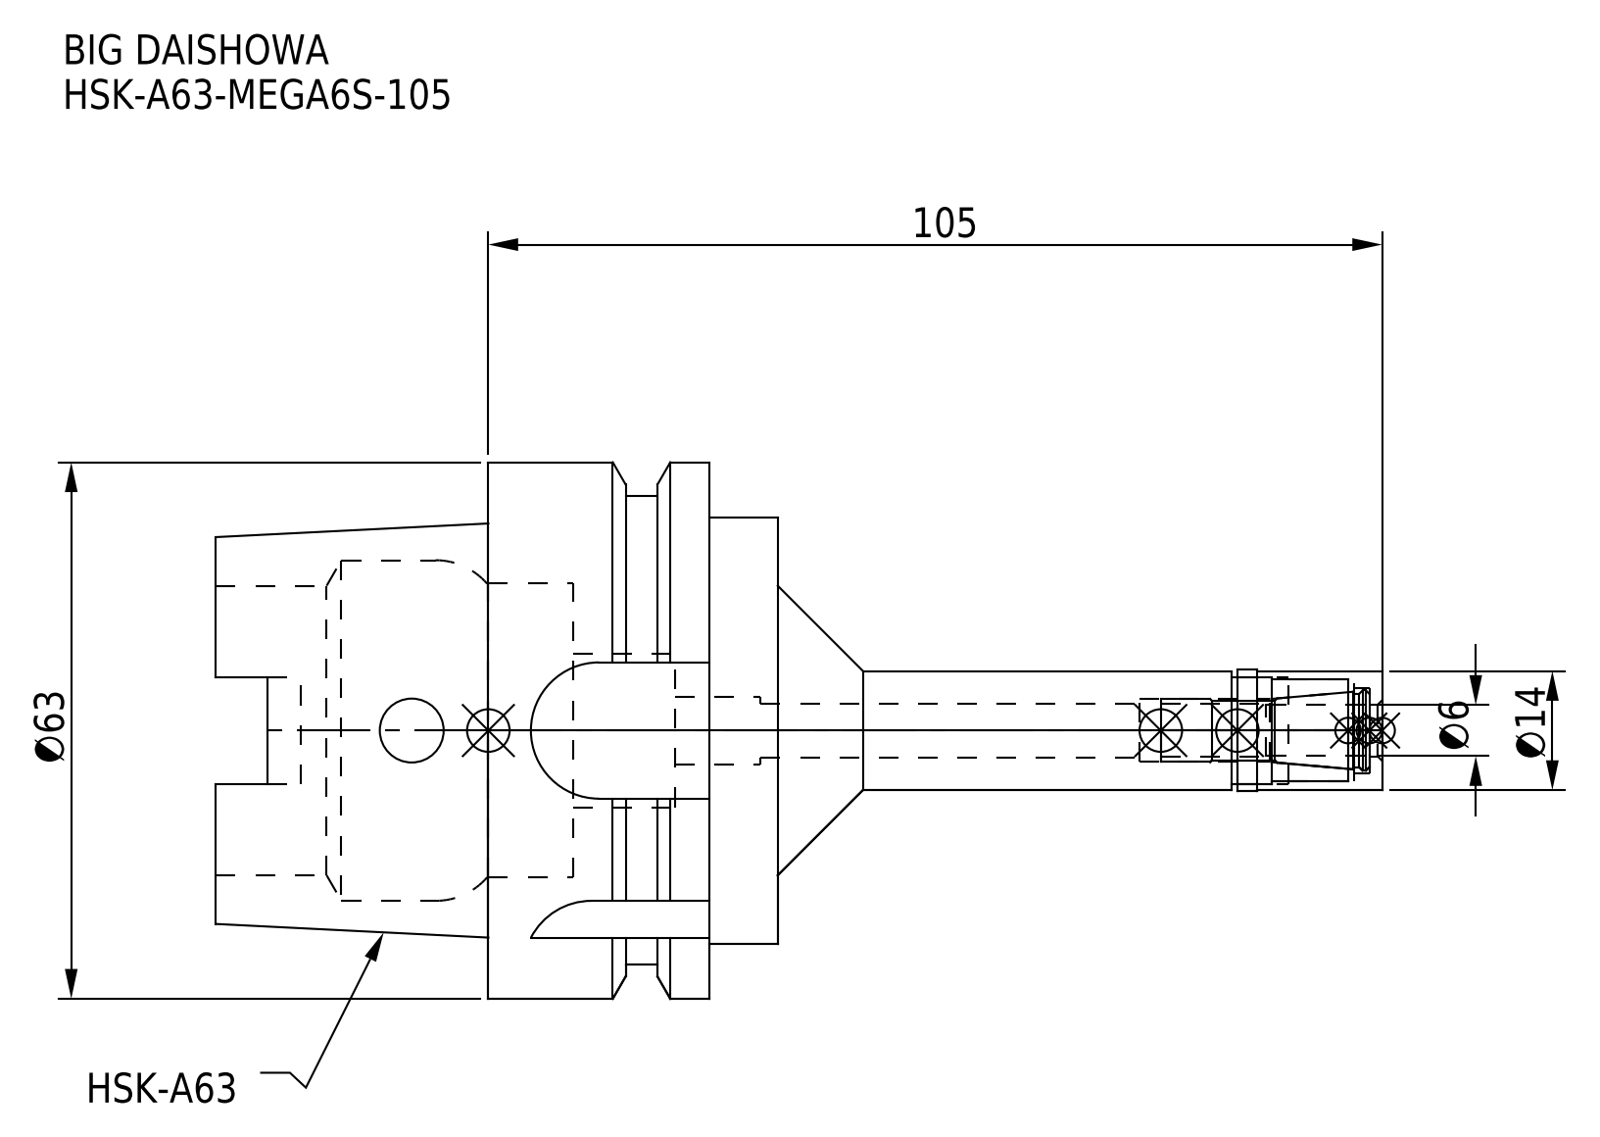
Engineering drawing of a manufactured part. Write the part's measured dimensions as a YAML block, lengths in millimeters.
part_name: "DXF_TEMP_ASSY_ASM_4_ASM.stp; HSK-A63-MEGA6S-105-060-FreeParts; HSK-A63-MEGA6S-105_1.stp; HSK-A63-MEGA6S-105-060.stp (+3 more)"
step_written_by: "SolidWorks 2019 (CONFIG_CONTROL_DESIGN)"
units: millimeters
bodies: {solids: 2, faces: 122, planar: 47, cylindrical: 55, other: 20}
overall_size: [137, 63, 63]
volume: 108320
surface_area: 29572
round_holes:
  - {diameter: 6.1, count: 1}
  - {diameter: 6.4, count: 1}
  - {diameter: 7.4, count: 1}
  - {diameter: 7.5, count: 1}
  - {diameter: 8, count: 1}
  - {diameter: 10, count: 1}
  - {diameter: 12, count: 1}
  - {diameter: 12.5, count: 1}
  - {diameter: 18, count: 1}
  - {diameter: 34, count: 1}
  - {diameter: 34.5, count: 1}
  - {diameter: 40, count: 1}
round_bosses_or_shafts:
  - {diameter: 63, count: 1}
  - {diameter: 55, count: 1}
  - {diameter: 50, count: 1}
  - {diameter: 14.3, count: 1}
  - {diameter: 14, count: 1}
partial_cylinders:
  - {radius: 2.88, count: 4}
  - {radius: 8, count: 4}
face_to_face_distances: [26, 34, 8, 24.05, 16.05, 9.95, 58, 32, 66, 41.95]
